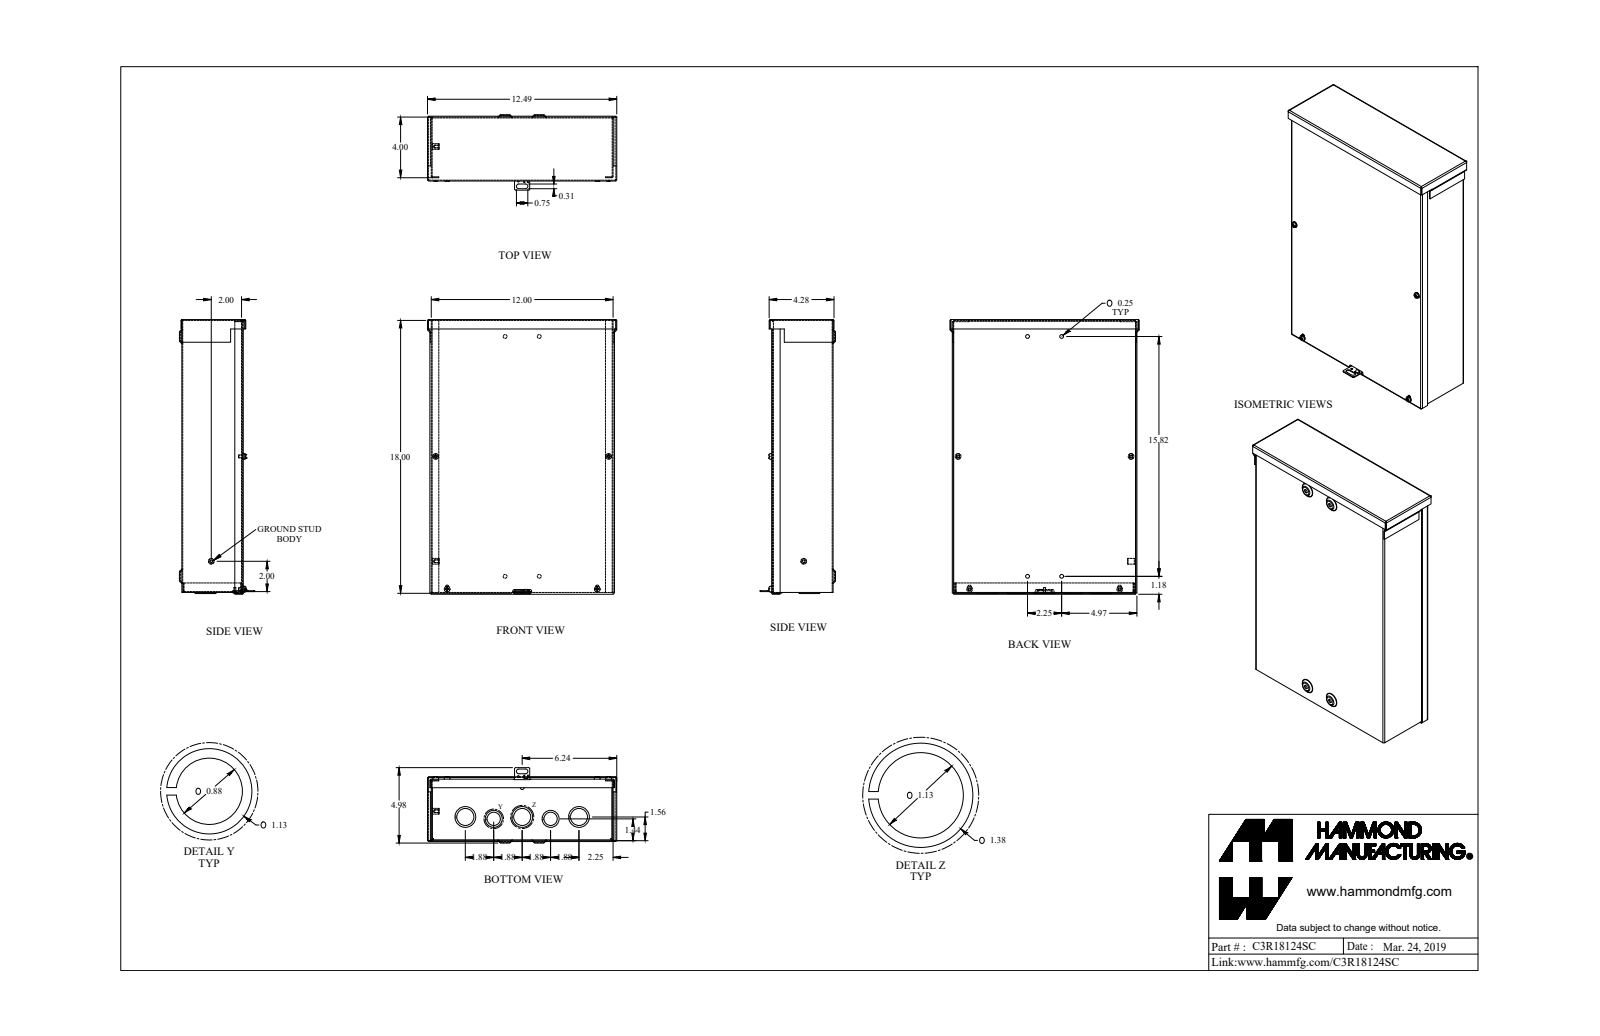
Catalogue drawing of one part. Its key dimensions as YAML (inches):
part_name: "C3R18124SC_Default"
step_written_by: "SolidWorks 2019 (CONFIG_CONTROL_DESIGN)"
units: inches
bodies: {solids: 11, faces: 429, planar: 226, cylindrical: 117, other: 86}
overall_size: [18.12, 12.489, 4.977]
volume: 43.51
surface_area: 1536
round_holes:
  - {diameter: 0.17, count: 4}
  - {diameter: 0.25, count: 4}
  - {diameter: 1.125, count: 3}
  - {diameter: 0.875, count: 2}
  - {diameter: 0.125, count: 1}
  - {diameter: 0.137, count: 1}
  - {diameter: 0.156, count: 1}
round_bosses_or_shafts:
  - {diameter: 0.19, count: 4}
  - {diameter: 0.375, count: 3}
  - {diameter: 1.375, count: 2}
  - {diameter: 1.125, count: 2}
  - {diameter: 0.375, count: 2}
  - {diameter: 1.375, count: 1}
  - {diameter: 0.125, count: 1}
partial_cylinders:
  - {radius: 0.029, count: 21}
  - {radius: 0.086, count: 21}
  - {radius: 0.109, count: 8}
  - {radius: 0.125, count: 8}
  - {radius: 0.156, count: 2}
face_to_face_distances: [0.057, 4, 3.943, 4.057, 11.943, 0.057, 12, 11.886, 17.886, 17.943]
hole_center_spacings: [9.141, 10.451, 1.879, 1.88, 2.25, 2.787, 3.75, 3.92]
